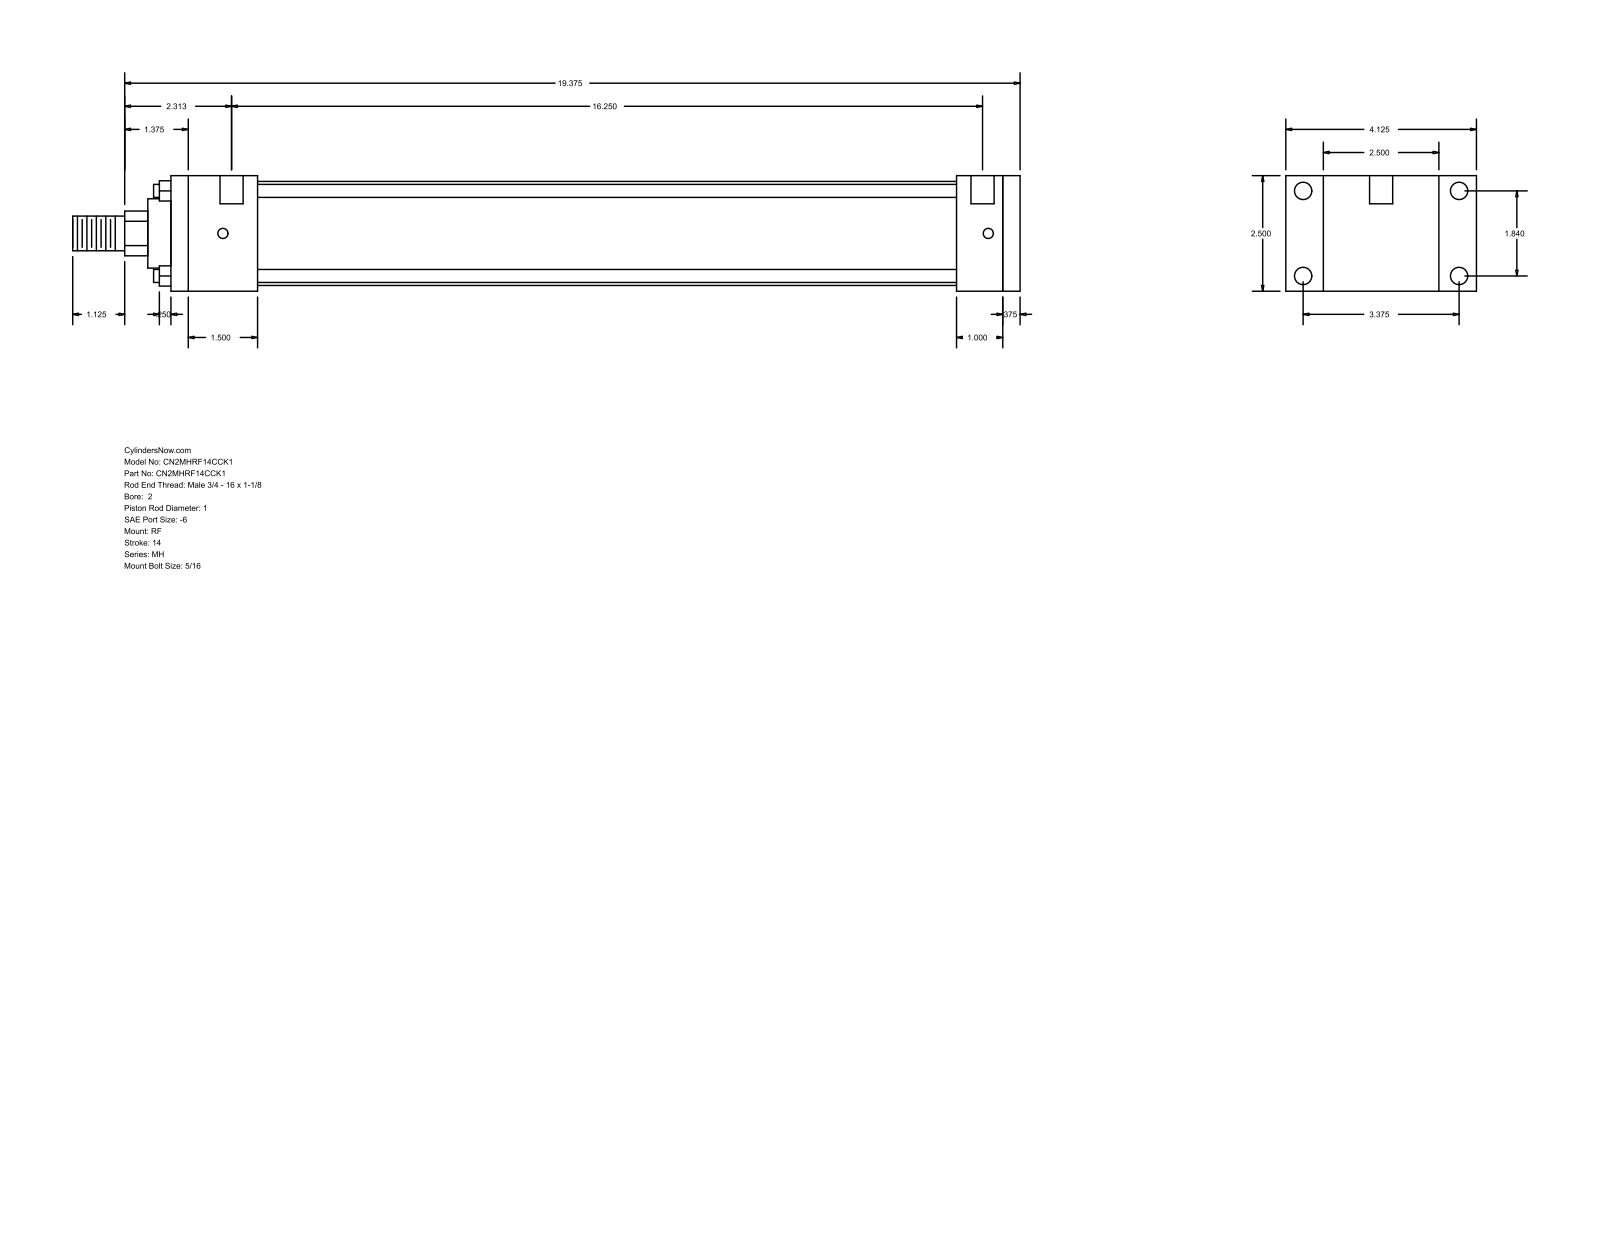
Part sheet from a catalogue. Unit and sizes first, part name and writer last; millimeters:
Units: millimetres
Overall size (bounding box): 520.7 × 104.78 × 63.5
Round holes (diameter × count): ⌀5.56 ×4, ⌀9.53 ×4, ⌀12.7 ×2
Round bosses / shafts (diameter × count): ⌀7.14 ×4, ⌀57.15 ×1, ⌀38.1 ×1, ⌀25.4 ×1, ⌀19.05 ×1
Partial cylindrical surfaces — rounded edges, fillets, slot ends (radius × count): R12.29 ×1
Main face-to-face distances: 63.5, 466.72, 9.52, 457.2, 20.64, 25.4, 47.63, 431.8, 384.17, 409.57
Hole centre spacings: 46.74, 85.72, 97.63, 420.68, 3.17, 4.76, 412.75, 415.92
Bodies: 0 solids, 92 faces (64 planar, 28 cylindrical, 0 other)
Part name (STEP PRODUCT): MH_RF__0200_1
STEP written by: GSSL Pune (CONFIG_CONTROL_DESIGN)
